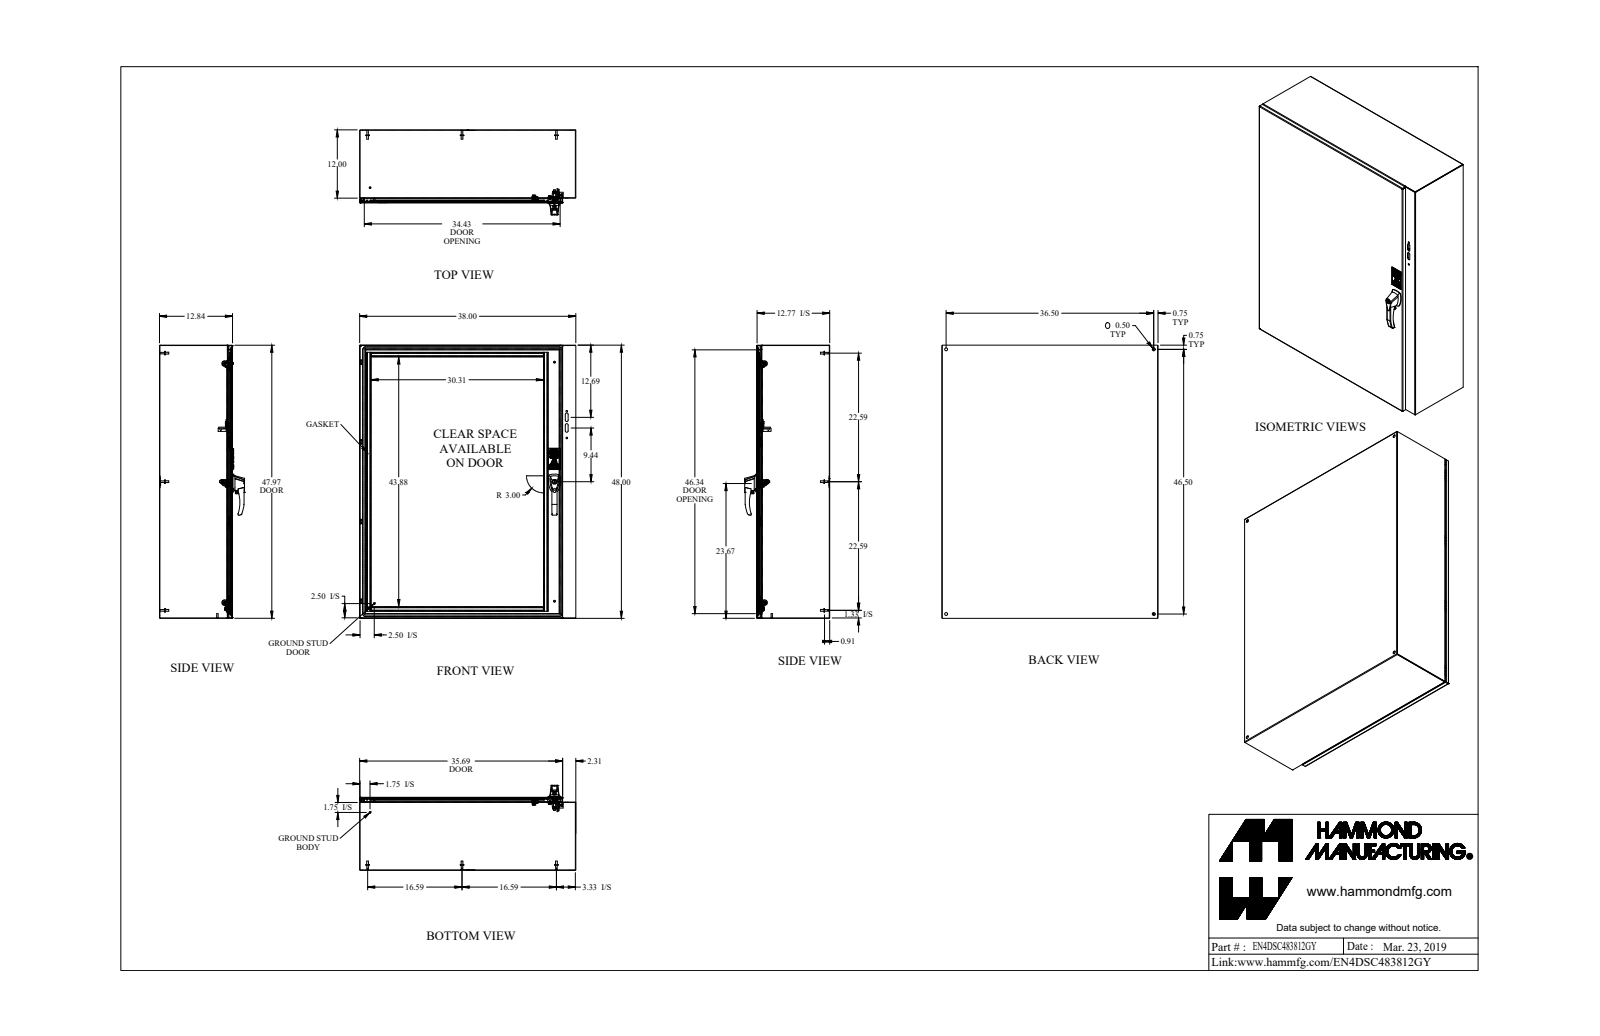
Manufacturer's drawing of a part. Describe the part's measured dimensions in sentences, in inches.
The part is named "EN4DSC483812GY". Its 3-D file was written by "SolidWorks 2019 (AUTOMOTIVE_DESIGN)". It is 75 solids with 1578 faces: 889 planar, 476 cylindrical and 213 other. Overall it measures 48 by 38 by 14.952 inches. Its volume is 481.2 cubic inches and its surface area 13 248 square inches. Round holes: 6 of diameter 0.176, 4 of diameter 0.5, 3 of diameter 0.196, 3 of diameter 0.25, 3 of diameter 0.265, 3 of diameter 0.413, 2 of diameter 0.156, 2 of diameter 0.172, 2 of diameter 0.173, 2 of diameter 0.215, 2 of diameter 0.256, 2 of diameter 0.281. Round bosses or shafts: 9 of diameter 0.25, 8 of diameter 0.625, 8 of diameter 0.313, 8 of diameter 0.27, 6 of diameter 0.156, 5 of diameter 0.375, 3 of diameter 1, 2 of diameter 0.63. Partial cylindrical surfaces (rounded edges, fillets, slot ends): 24 of radius 0.043, 24 of radius 0.081, 18 of radius 0.036, 18 of radius 0.108, 17 of radius 0.062, 15 of radius 0.25, 14 of radius 0.03, 14 of radius 0.125. The main face-to-face distances are 0.072, 12.765, 12.693, 12.837, 37.928, 47.928, 37.856, 38, 47.856, 48. The hole center spacings are 21, 1.11, 2.883, 21, 21.001, 32.722, 36.5, 42.001.
